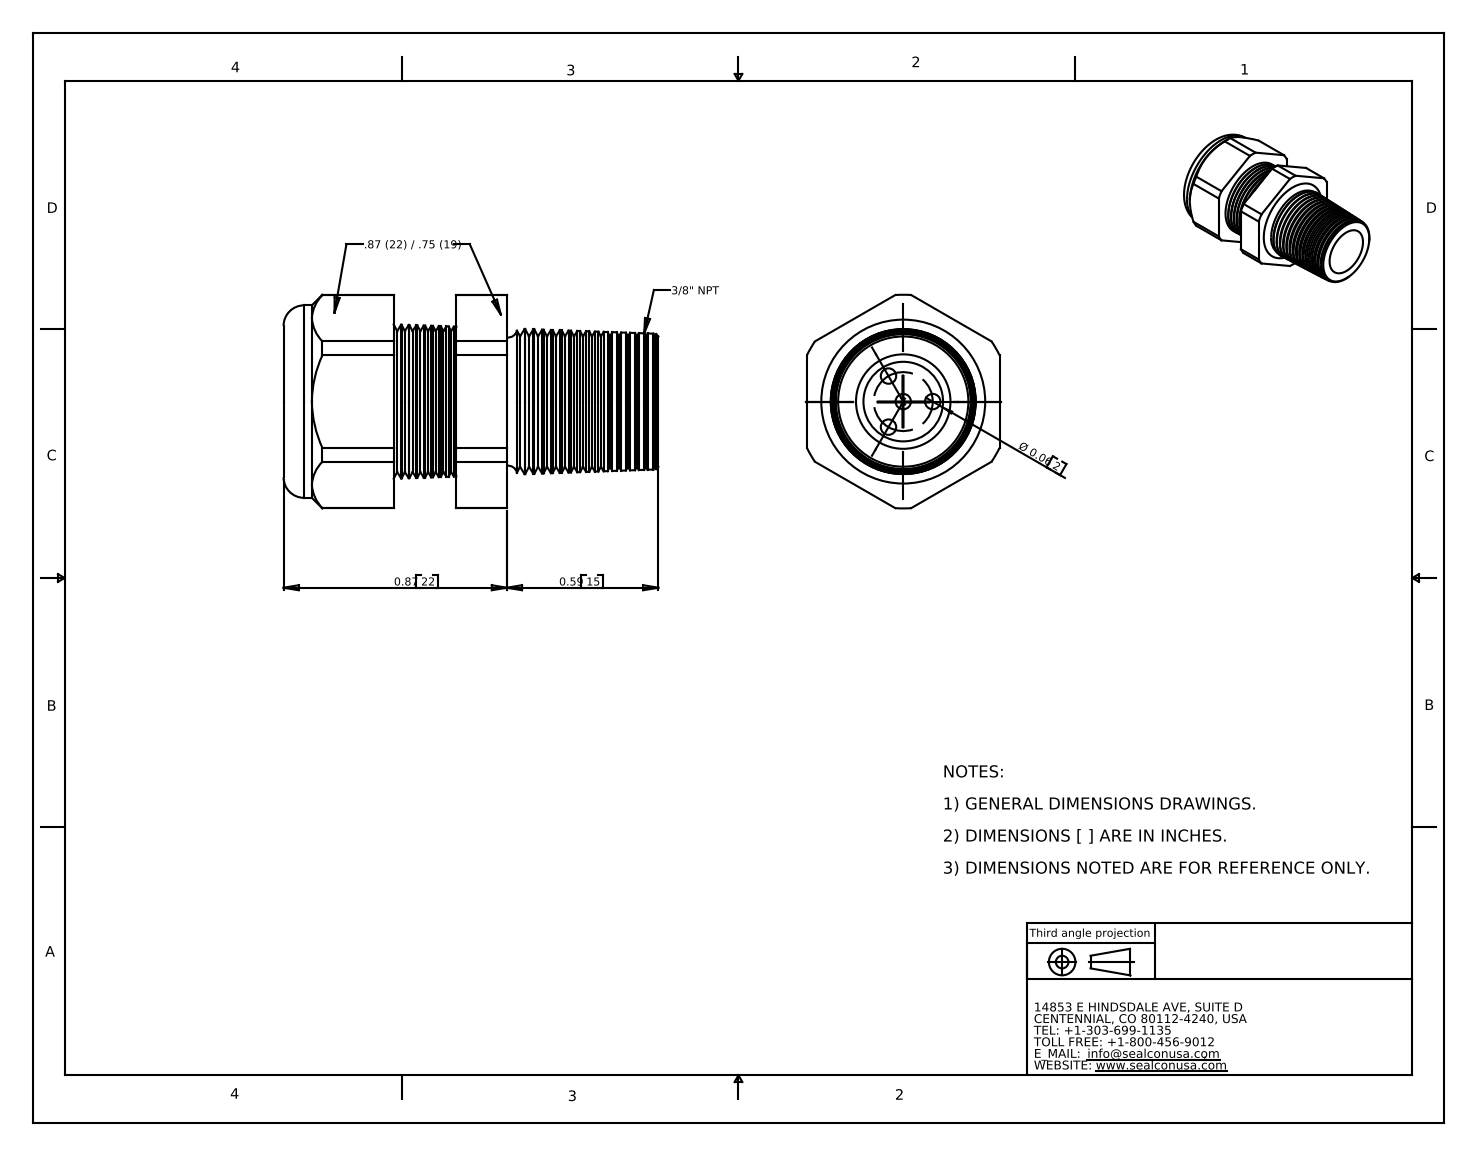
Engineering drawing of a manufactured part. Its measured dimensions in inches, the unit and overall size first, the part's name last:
Units: inches
Overall size (bounding box): 1.46 × 0.833 × 0.75
Round holes (diameter × count): ⌀0.06 ×4, ⌀0.29 ×1, ⌀0.31 ×1
Round bosses / shafts (diameter × count): ⌀0.75 ×1
Partial cylindrical surfaces — rounded edges, fillets, slot ends (radius × count): R0.416 ×1
Main face-to-face distances: 0.75, 0.673, 0.429, 0.244, 0.75, 0.87, 0.441, 0.197, 1.46, 1.031
Hole centre spacings: 0.115, 0.199
Volume: 0.369 in³ · Surface area: 7.033 in²
Bodies: 2 solids, 206 faces (20 planar, 28 cylindrical, 158 other)
Part name (STEP PRODUCT): CD09N1-BK
STEP written by: SolidWorks 2007 (CONFIG_CONTROL_DESIGN)
